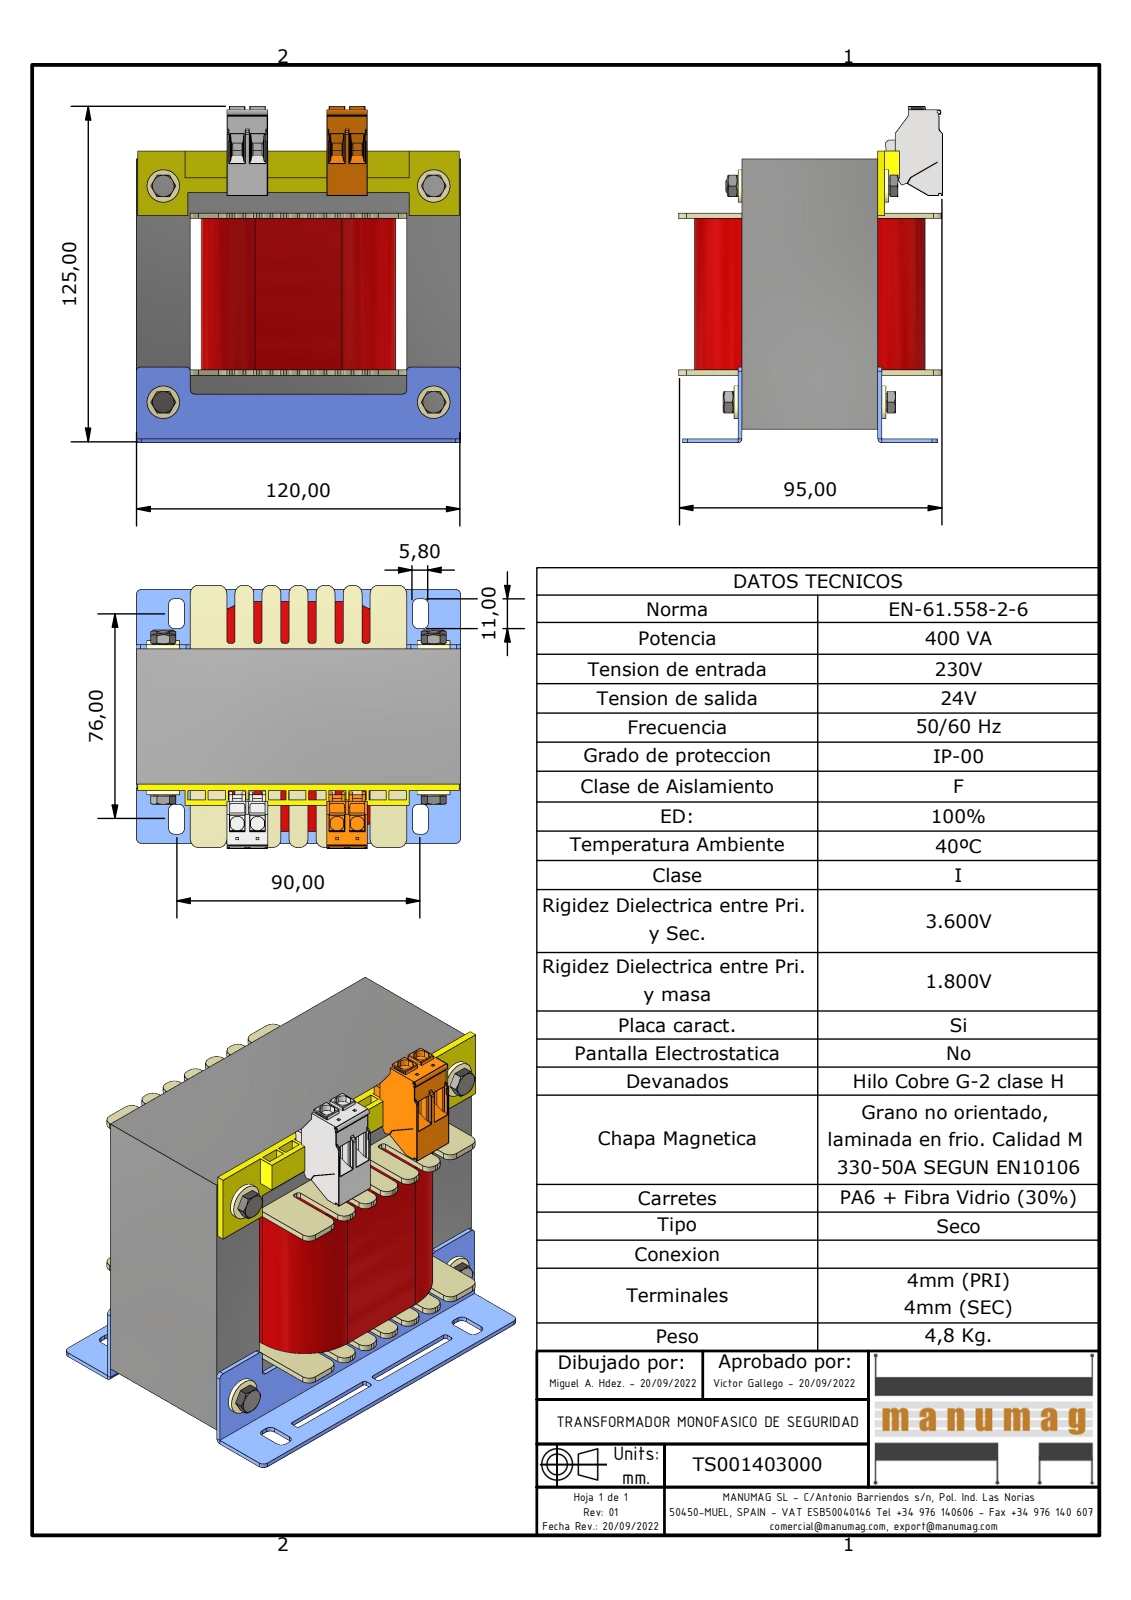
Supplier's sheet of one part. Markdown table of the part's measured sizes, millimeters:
| quantity | value |
| --- | --- |
| part name | TS001403000; EI120 x 100 - 50 (Rc40); AF40DIN; EI120 (+6 more) |
| STEP written by | Autodesk Inventor 2023 (AUTOMOTIVE_DESIGN) |
| units | millimeters |
| bodies | 23 solids, 3877 faces (3067 planar, 568 cylindrical, 242 other) |
| overall size | 124.5 × 120 × 97.4 |
| volume | 742 103 mm³ |
| surface area | 153 201 mm² |
| round holes (diameter × count) | 4.13 × 4, 5 × 4, 6.6 × 4, 6.8 × 2 |
| round bosses / shafts (diameter × count) | 12 × 4, 6.7 × 4, 5.9 × 4, 4.57 × 4 |
| partial cylindrical surfaces (radius × count) | 0.15 × 160, 0.2 × 48, 1 × 28, 3 × 28, 2 × 20, 0.8 × 17, 0.5 × 12, 0.3 × 7 |
| main face-to-face distances | 80, 20, 40, 50, 60, 100, 1.5, 16, 56, 85 |
| hole center spacings | 80, 100, 128.06 |
